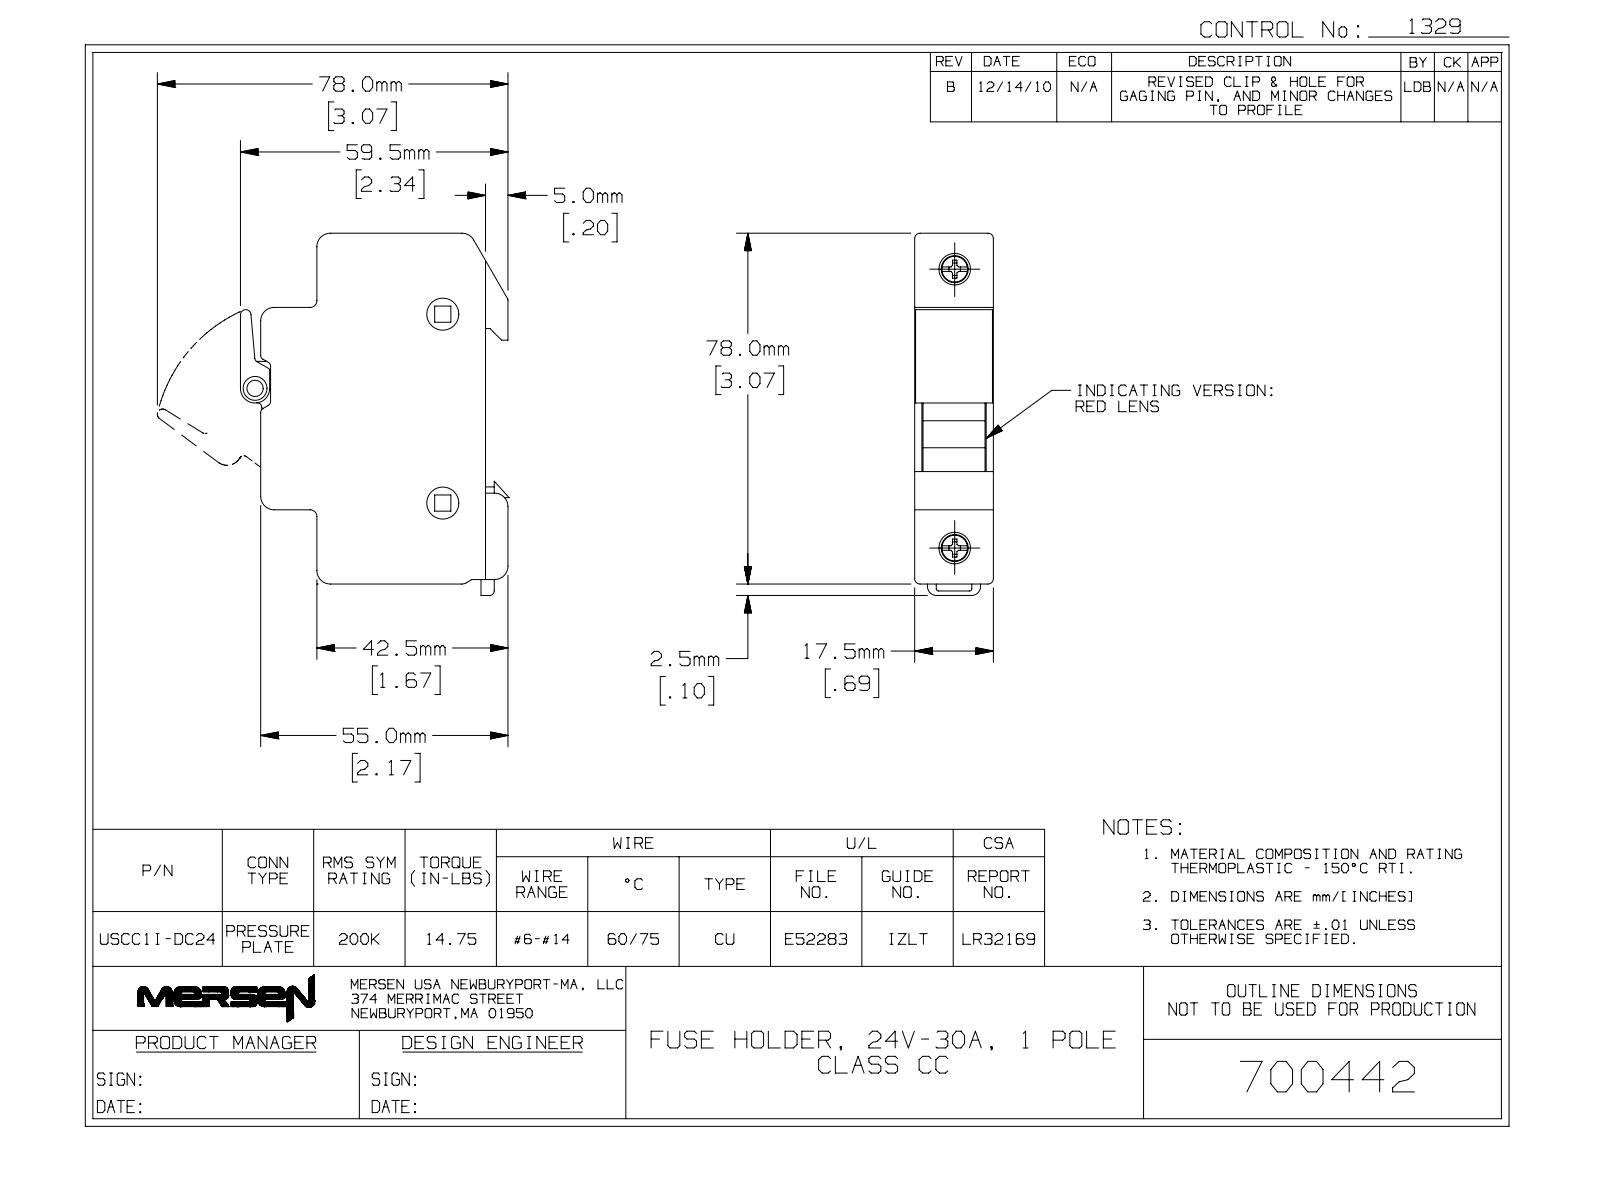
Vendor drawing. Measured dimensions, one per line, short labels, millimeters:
name: USCC1I-DC24; MR8.017.000.1～4 档板（头盖浅灰A8）RT18M-32; 12. USCC载熔件SLDPRT
written by: SolidWorks 2021 (CONFIG_CONTROL_DESIGN)
unit: mm
bodies: 24 solids, 2884 faces (1764 planar, 530 cylindrical, 590 other)
size: 80 × 60 × 17.6
volume: 27 658 mm³; area: 43 078 mm²
holes: 4× ⌀7.2, 2× ⌀4.2, 2× ⌀6.5, 1× ⌀2, 1× ⌀3, 1× ⌀3.23, 1× ⌀5.2, 1× ⌀5.4
bosses: 8× ⌀1.5, 3× ⌀5, 2× ⌀8.4, 2× ⌀6.5, 2× ⌀3.6, 1× ⌀9, 1× ⌀2.5
rounds: 66× R0.5, 58× R0.3, 43× R1, 20× R0.6, 15× R2, 12× R1.5, 12× R1.6, 7× R3
face distances: 1.6, 16, 17.6, 14.4, 0.6, 13.8, 2, 2.2, 0.8, 1.1
hole spacings: 61.82, 5.35, 16, 16.11, 17.75, 17.83, 36.36, 36.4
